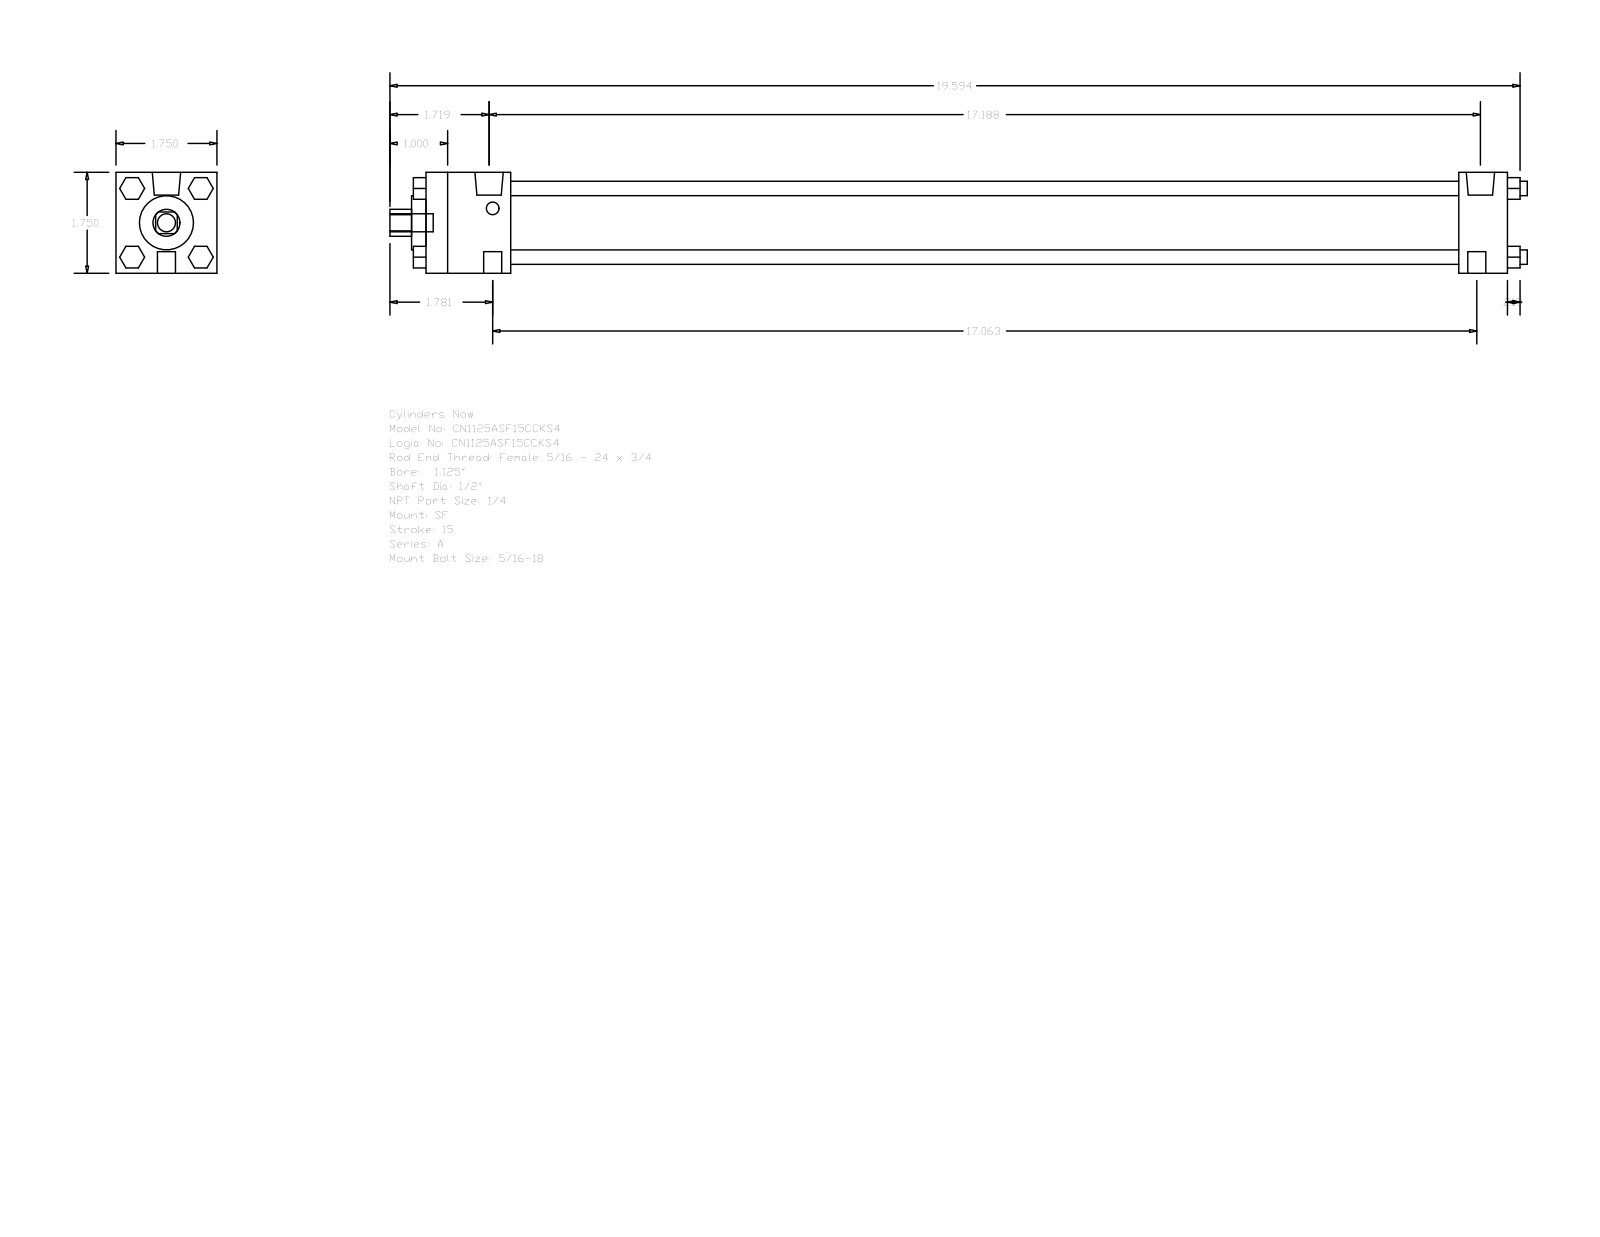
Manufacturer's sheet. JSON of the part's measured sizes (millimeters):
{"part_name": "A_SF__0112_0.5", "step_written_by": "GSSL Pune (CONFIG_CONTROL_DESIGN)", "units": "millimeters", "bodies": {"solids": 0, "faces": 120, "planar": 92, "cylindrical": 28, "other": 0}, "overall_size": [500.86, 44.45, 44.45], "round_holes": [[12.7, 1], [23.81, 1], [31.88, 1]], "round_bosses_or_shafts": [[6.35, 4], [7.94, 3], [12.49, 2], [5.56, 2]], "partial_cylinders_radius": [[5.94, 1]], "face_to_face_distances": [44.46, 476.24, 454.81, 21.43, 37.3, 417.51, 438.94, 9.53, 5.59, 9.52]}
